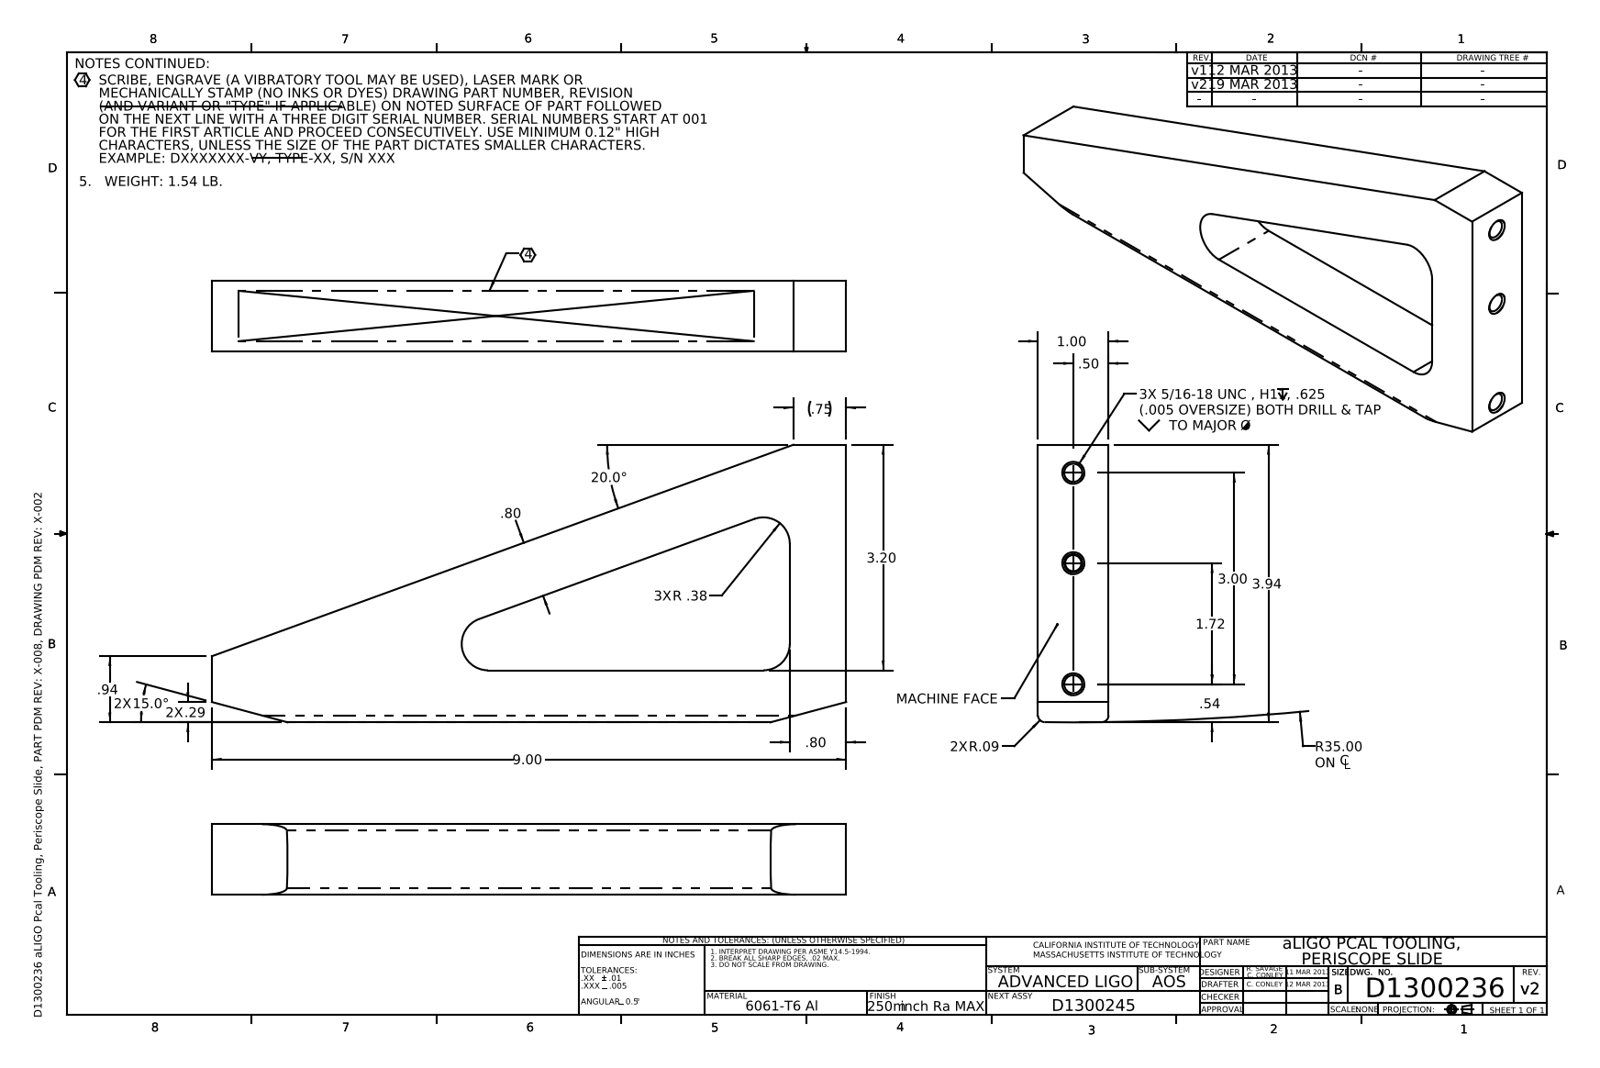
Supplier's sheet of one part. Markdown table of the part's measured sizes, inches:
| quantity | value |
| --- | --- |
| part name | D1300236-v2 aLIGO Pcal Tooling, Periscope Slide |
| STEP written by | SolidWorks 2013 (AUTOMOTIVE_DESIGN) |
| units | inches |
| bodies | 1 solid, 36 faces (11 planar, 13 cylindrical, 12 other) |
| overall size | 9 × 3.938 × 1 |
| volume | 15.82 in³ |
| surface area | 67.92 in² |
| round holes (diameter × count) | 0.257 × 3 |
| partial cylindrical surfaces (radius × count) | 0.375 × 3, 0.094 × 2, 35 × 1 |
| main face-to-face distances | 1, 0.8, 3.2, 8.2, 9 |
| hole center spacings | 1.282, 1.718, 3 |
